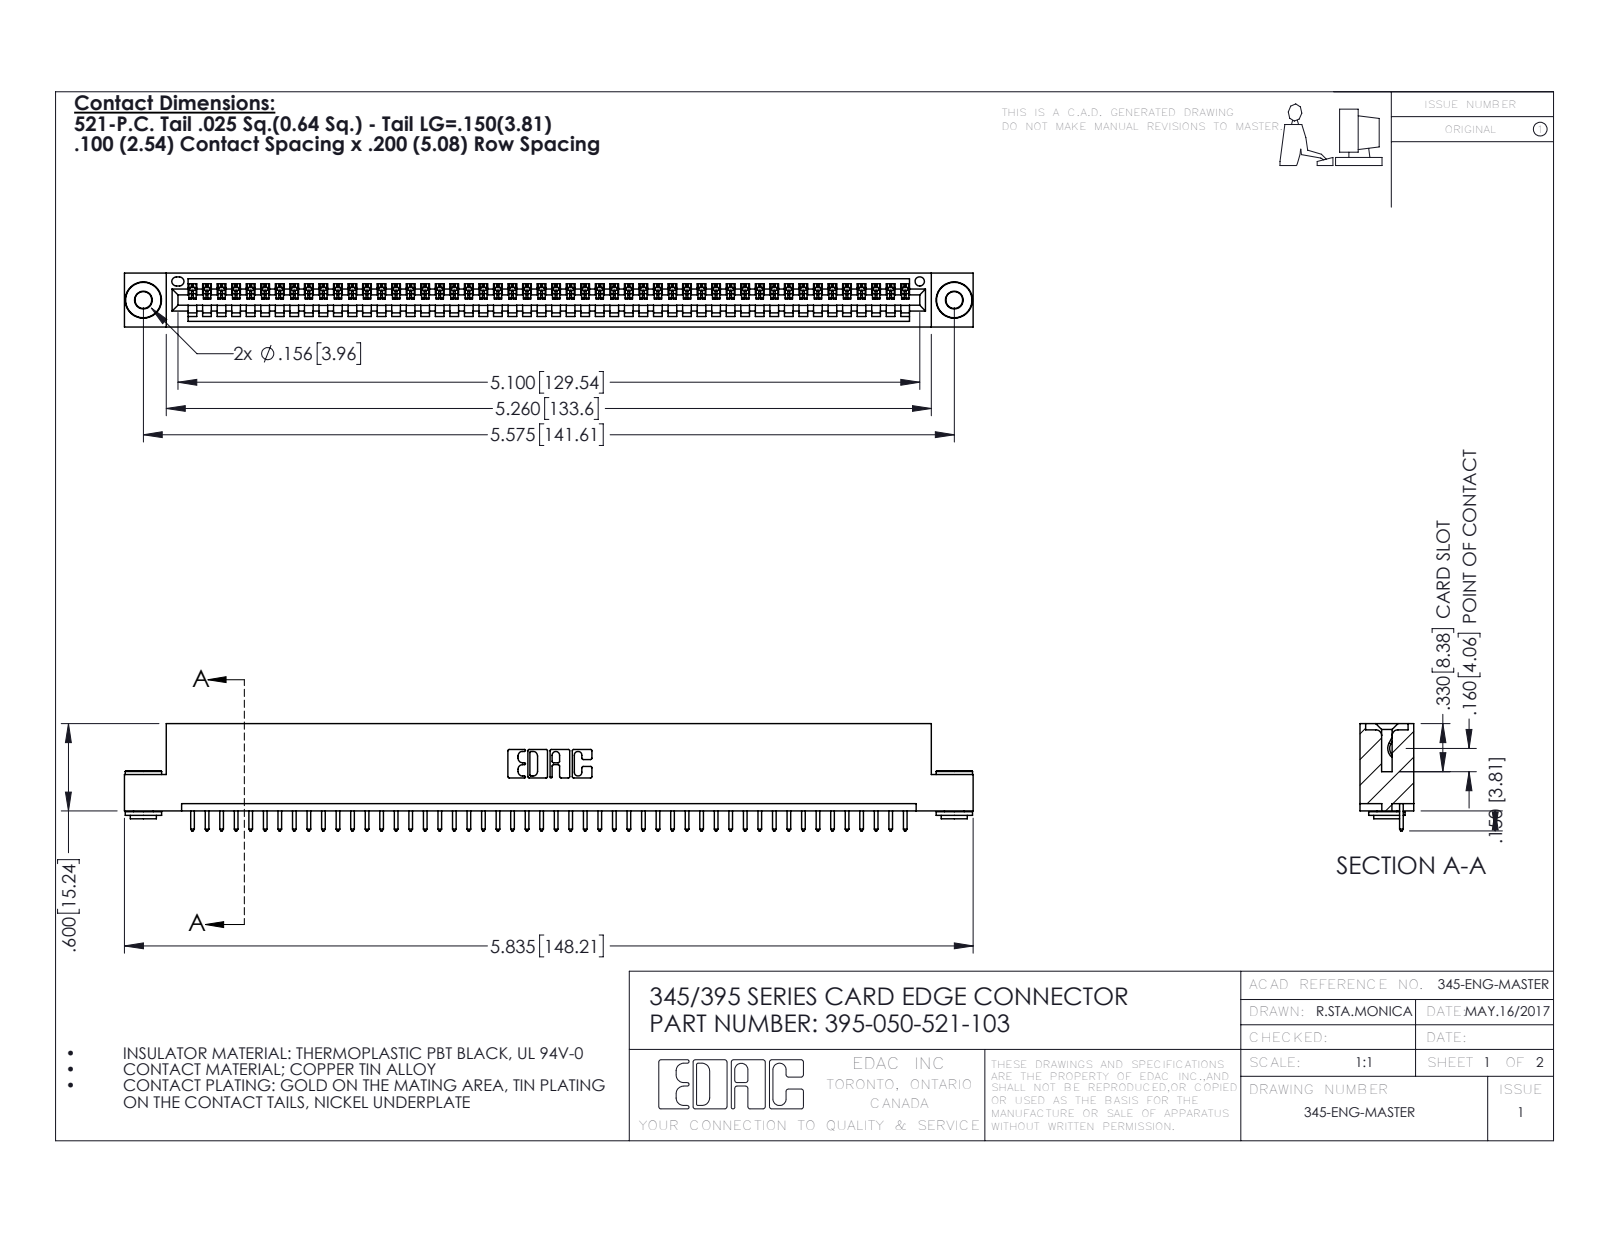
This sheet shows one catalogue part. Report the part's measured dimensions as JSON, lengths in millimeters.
{"part_name": "395-050-521-103; 345 Part_Flush Mounting Lugs - 0.156 Dia-TH; 345-250-002_345-250-002-102; 345-292-001_345-293-121", "step_written_by": "SolidWorks 2016 (CONFIG_CONTROL_DESIGN)", "units": "millimeters", "bodies": {"solids": 53, "faces": 3064, "planar": 2090, "cylindrical": 966, "other": 8}, "overall_size": [148.2, 18.7, 9.4], "volume_mm3": 14000, "surface_area_mm2": 18400, "round_holes": [[2.9, 2], [4, 2], [1.6, 1]], "round_bosses_or_shafts": [[6.4, 2], [4.6, 2], [3.5, 2]], "partial_cylinders_radius": [[0.2, 100], [0.3, 100], [0.3, 22], [0.2, 6], [0.8, 6], [0.7, 3], [0.8, 2], [1, 2]], "face_to_face_distances": [1.8, 7.6, 9.4, 5.1, 0.6, 2.5, 6.9, 5.7, 3.8, 1.8], "hole_center_spacings": [6.9, 135.6, 141.6]}
